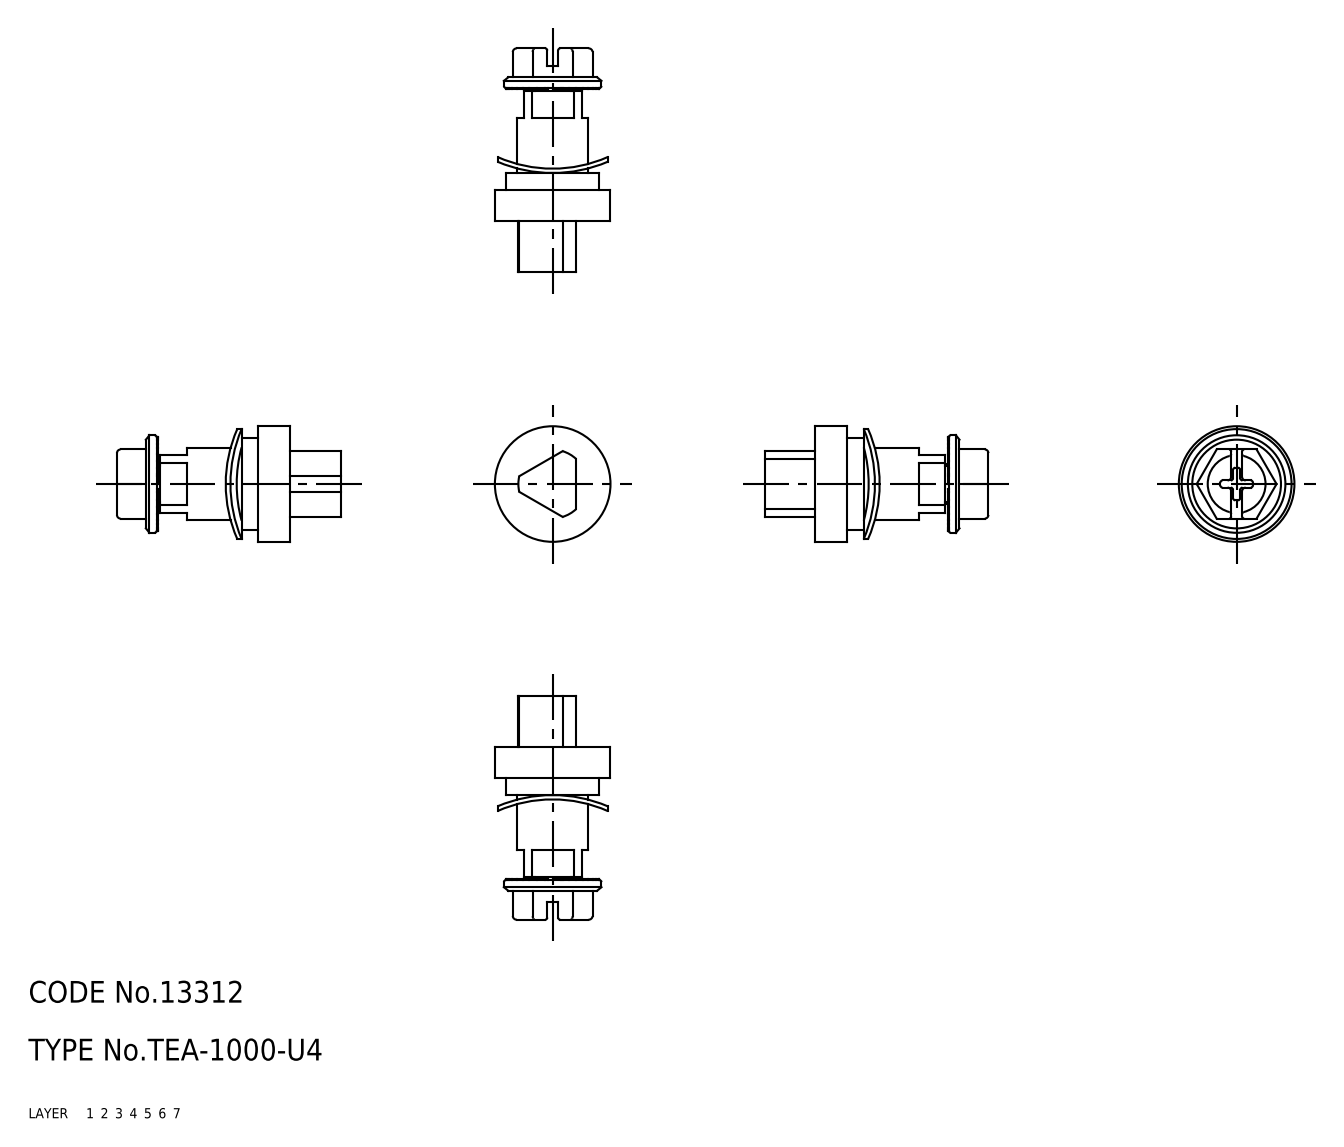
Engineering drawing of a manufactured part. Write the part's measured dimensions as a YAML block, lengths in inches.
part_name: "shaft"
step_written_by: "CADfix (AUTOMOTIVE_DESIGN)"
units: inches
bodies: {solids: 1, faces: 138, planar: 0, cylindrical: 0, other: 138}
overall_size: [1.219, 0.63, 0.63]
volume: 0.175
surface_area: 3.046
